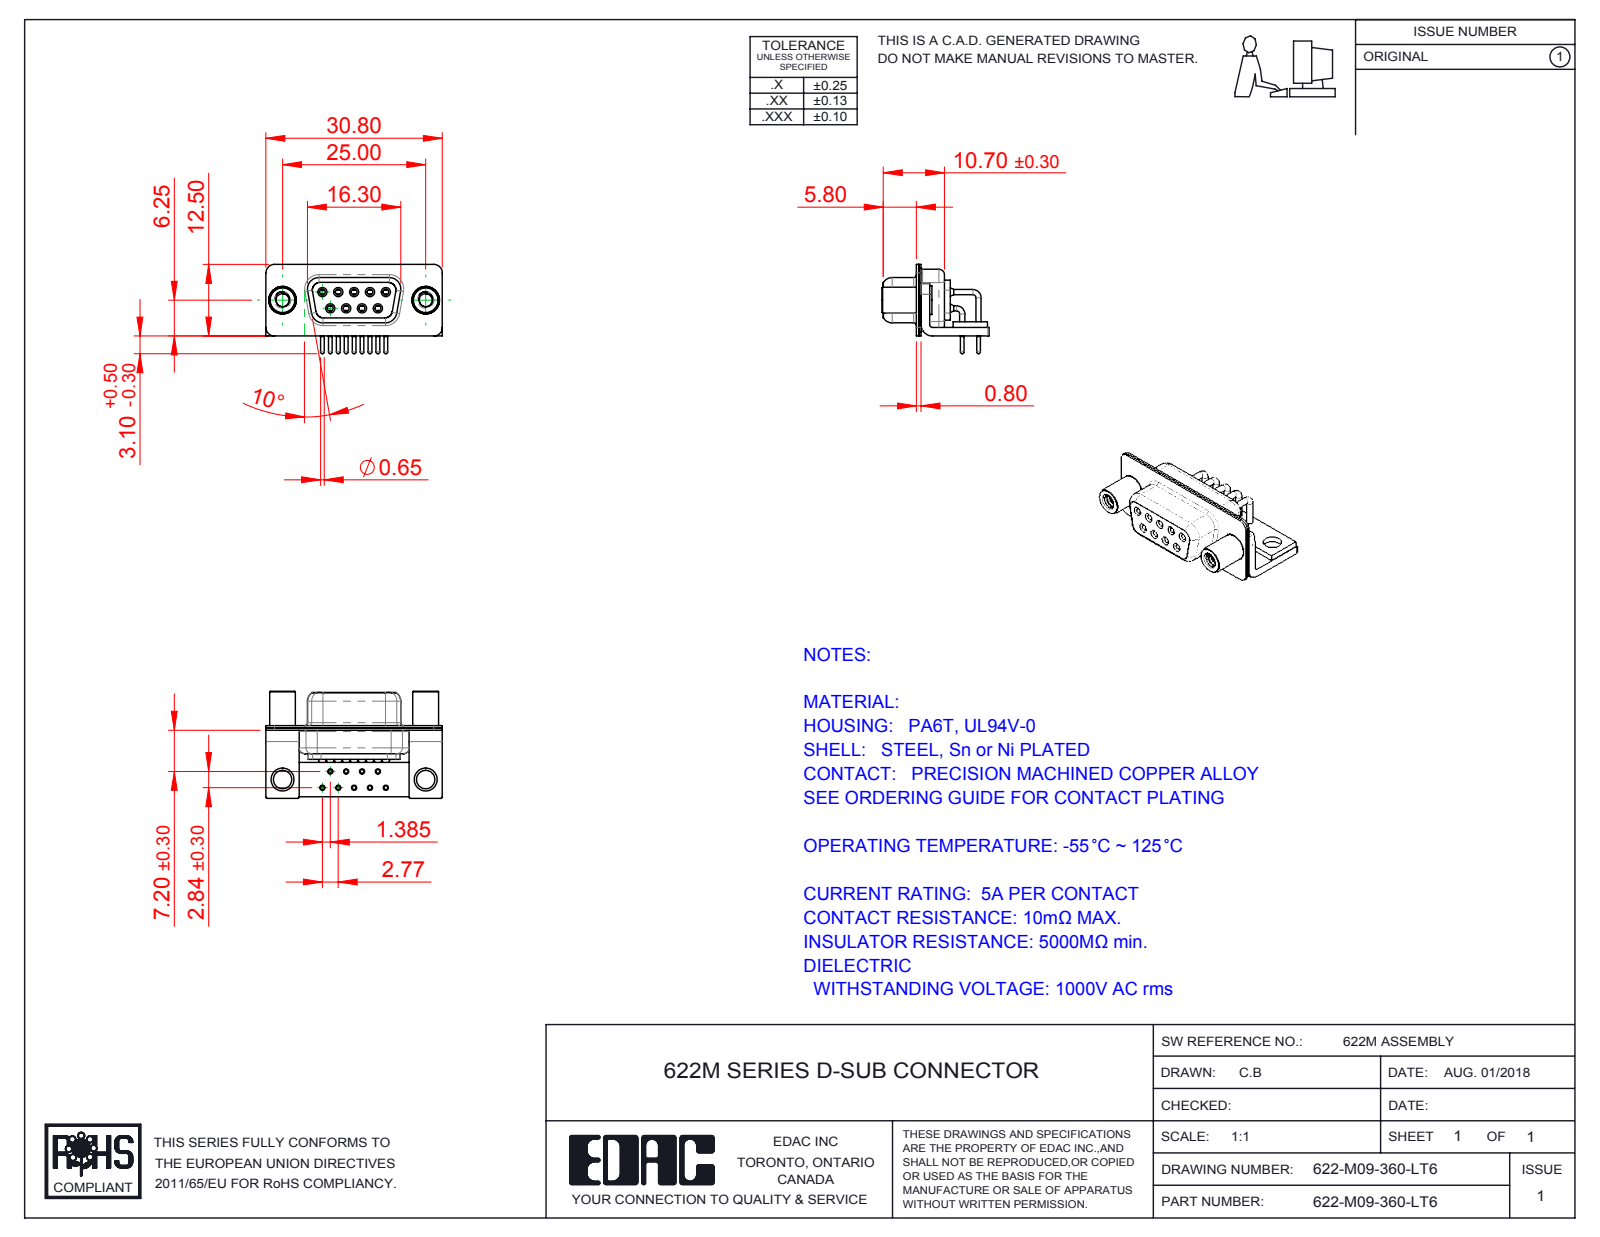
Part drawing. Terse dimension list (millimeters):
name: 622-M09-360-LT6; 622M Stabilizer Board_09 Contacts; 622M 4-40 Threaded Standoff; 622M Stabilizer Bracket (+5 more)
written by: SolidWorks 2016 (CONFIG_CONTROL_DESIGN)
unit: mm
bodies: 17 solids, 874 faces (230 planar, 426 cylindrical, 218 other)
size: 30.8 × 18.7 × 15.6
volume: 2 258 mm³; area: 5 841 mm²
holes: 9× ⌀0.9, 9× ⌀1, 9× ⌀1.1, 9× ⌀1.7, 9× ⌀1.8, 9× ⌀2, 2× ⌀2.26, 2× ⌀3.2, 2× ⌀4, 2× ⌀4.8
bosses: 9× ⌀1.6, 9× ⌀1.5, 9× ⌀0.9, 9× ⌀0.65, 2× ⌀5, 2× ⌀4.9, 2× ⌀4.5
rounds: 16× R0.25, 16× R1.5, 13× R2, 8× R1.35, 8× R1.6, 5× R0.5, 4× R0.6, 4× R0.65
face distances: 0.4, 0.8, 2.3, 1.9, 1.5, 1, 9.35, 1.45, 8.5, 8.95
hole spacings: 3.16, 2.77, 5.54, 5.03, 5.04, 8.31, 7.48, 7.49
